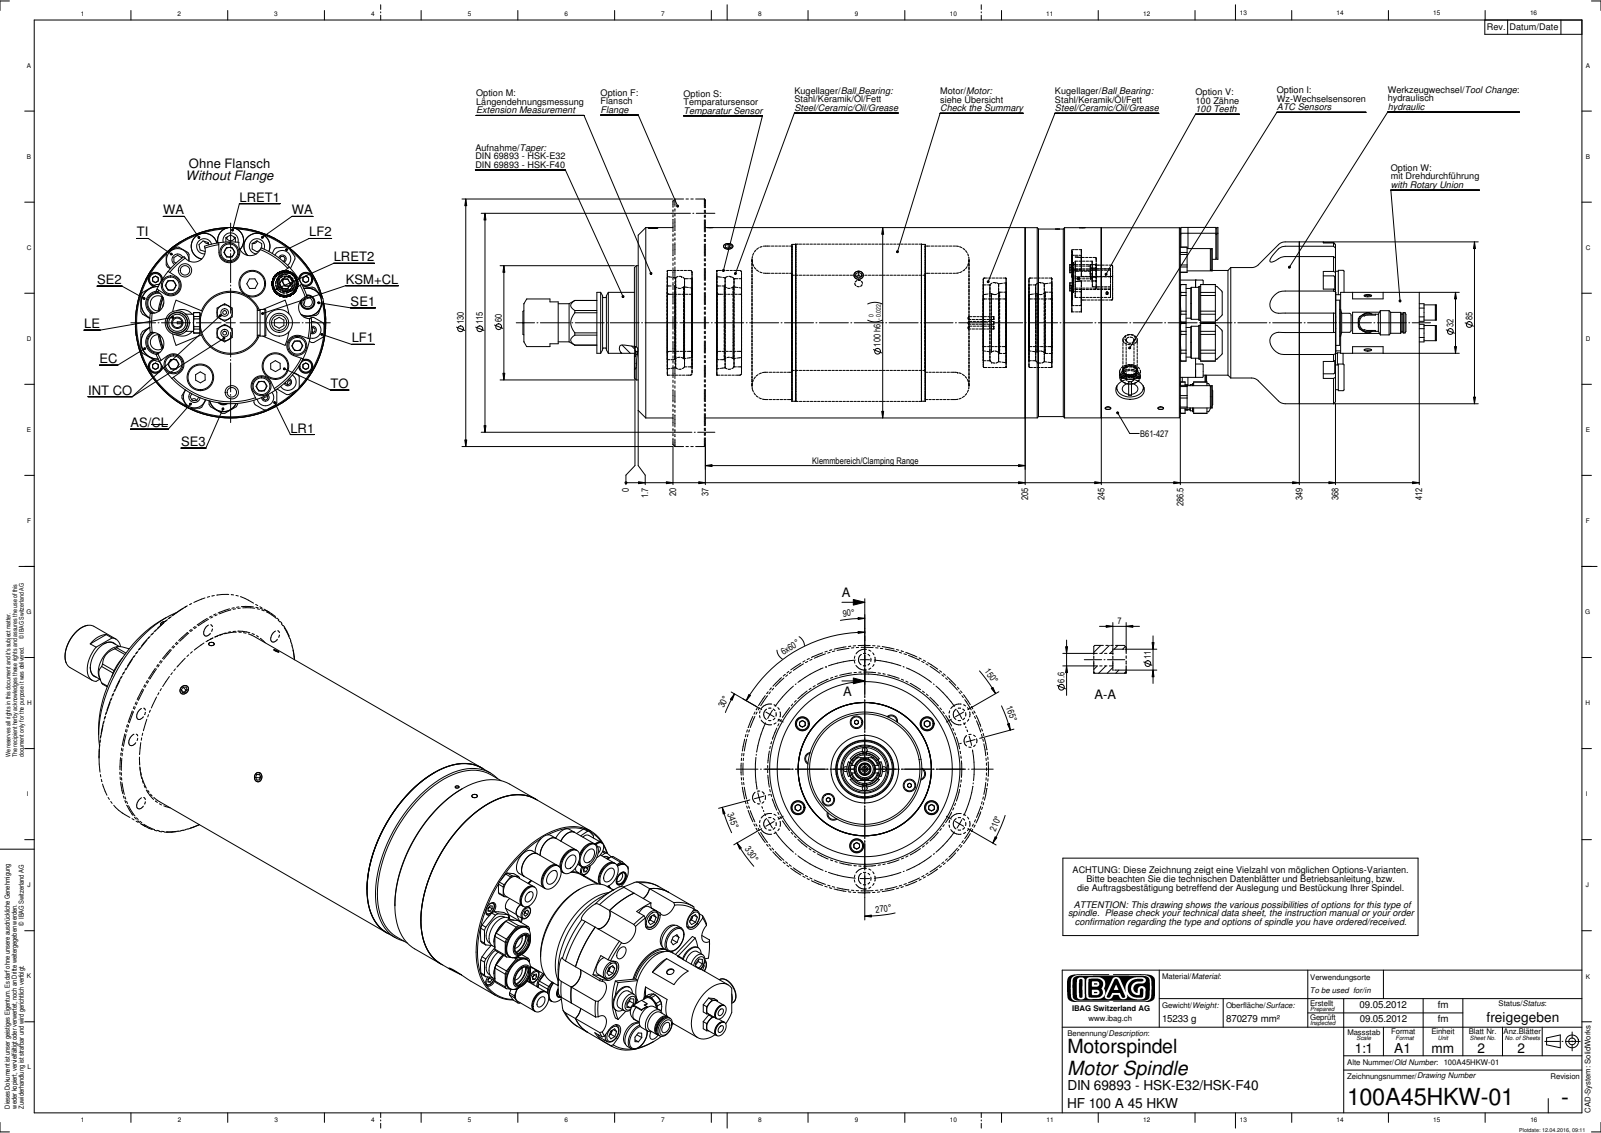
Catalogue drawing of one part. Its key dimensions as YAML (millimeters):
part_name: "100A45HKW-01"
step_written_by: "SolidWorks 2014 (CONFIG_CONTROL_DESIGN)"
units: millimeters
bodies: {solids: 0, faces: 1178, planar: 480, cylindrical: 459, other: 239}
overall_size: [479.86, 100.1, 100]
round_holes:
  - {diameter: 5, count: 12}
  - {diameter: 4, count: 10}
  - {diameter: 7.4, count: 9}
  - {diameter: 8, count: 6}
  - {diameter: 4.5, count: 3}
  - {diameter: 6, count: 3}
  - {diameter: 15, count: 3}
  - {diameter: 6.7, count: 2}
  - {diameter: 7, count: 2}
  - {diameter: 10.7, count: 2}
  - {diameter: 16.2, count: 2}
  - {diameter: 10, count: 1}
round_bosses_or_shafts:
  - {diameter: 10, count: 8}
  - {diameter: 14, count: 7}
  - {diameter: 5.7, count: 7}
  - {diameter: 13.7, count: 4}
  - {diameter: 13.7, count: 4}
  - {diameter: 8.8, count: 4}
  - {diameter: 7, count: 4}
  - {diameter: 13, count: 3}
partial_cylinders:
  - {radius: 5, count: 7}
  - {radius: 5.5, count: 6}
  - {radius: 6.6, count: 6}
  - {radius: 6, count: 5}
  - {radius: 8.25, count: 2}
  - {radius: 9.9, count: 2}
  - {radius: 5.4, count: 1}
  - {radius: 11.75, count: 1}
face_to_face_distances: [243.3, 81.5, 41.5, 284.8, 366.3, 123, 225, 18.3, 266.5, 348]
hole_center_spacings: [43.25, 45.6, 39, 39.5, 40.5, 72.27, 72.54, 5.1]
